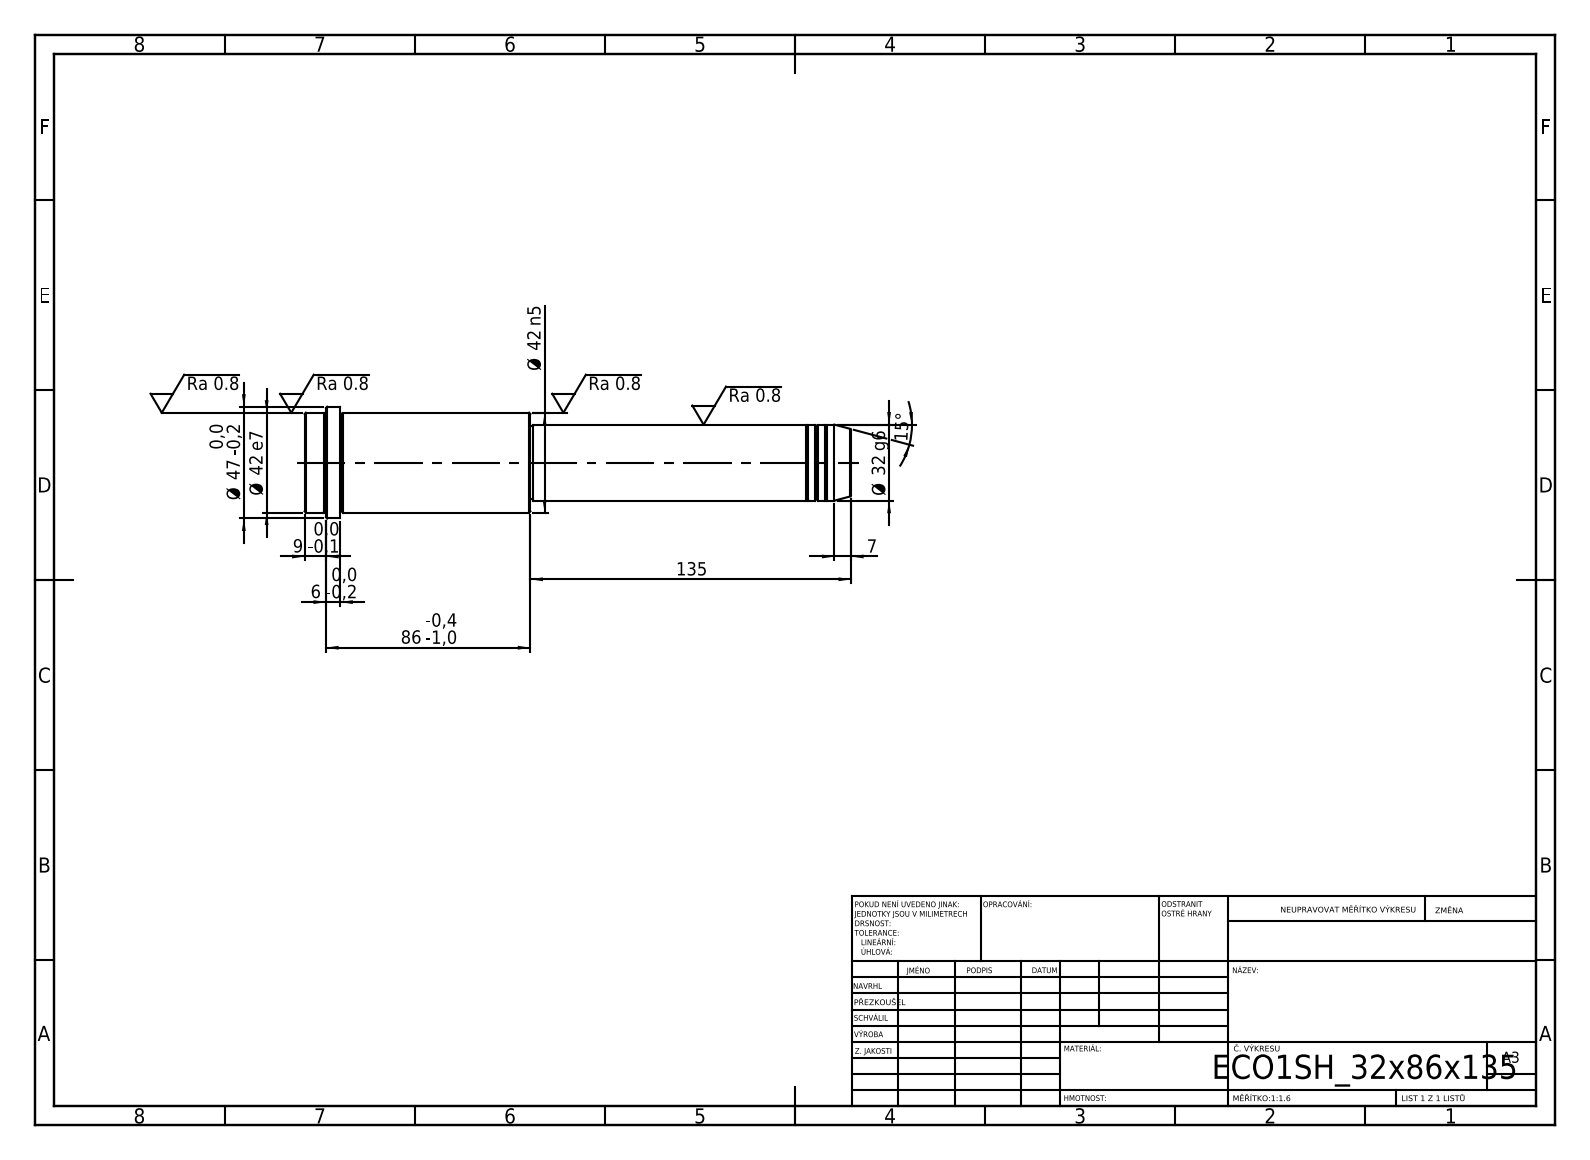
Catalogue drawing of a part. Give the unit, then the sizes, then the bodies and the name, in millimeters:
Units: millimetres
Overall size (bounding box): 230 × 47 × 47
Round bosses / shafts (diameter × count): ⌀47 ×1, ⌀42 ×1, ⌀32 ×1, ⌀31 ×1
Main face-to-face distances: 230, 135, 95, 215, 80, 15, 221, 86, 6, 9
Volume: 241 331 mm³ · Surface area: 29 747 mm²
Bodies: 1 solid, 52 faces (6 planar, 16 cylindrical, 30 other)
STEP written by: SolidWorks 2019 (CONFIG_CONTROL_DESIGN)
